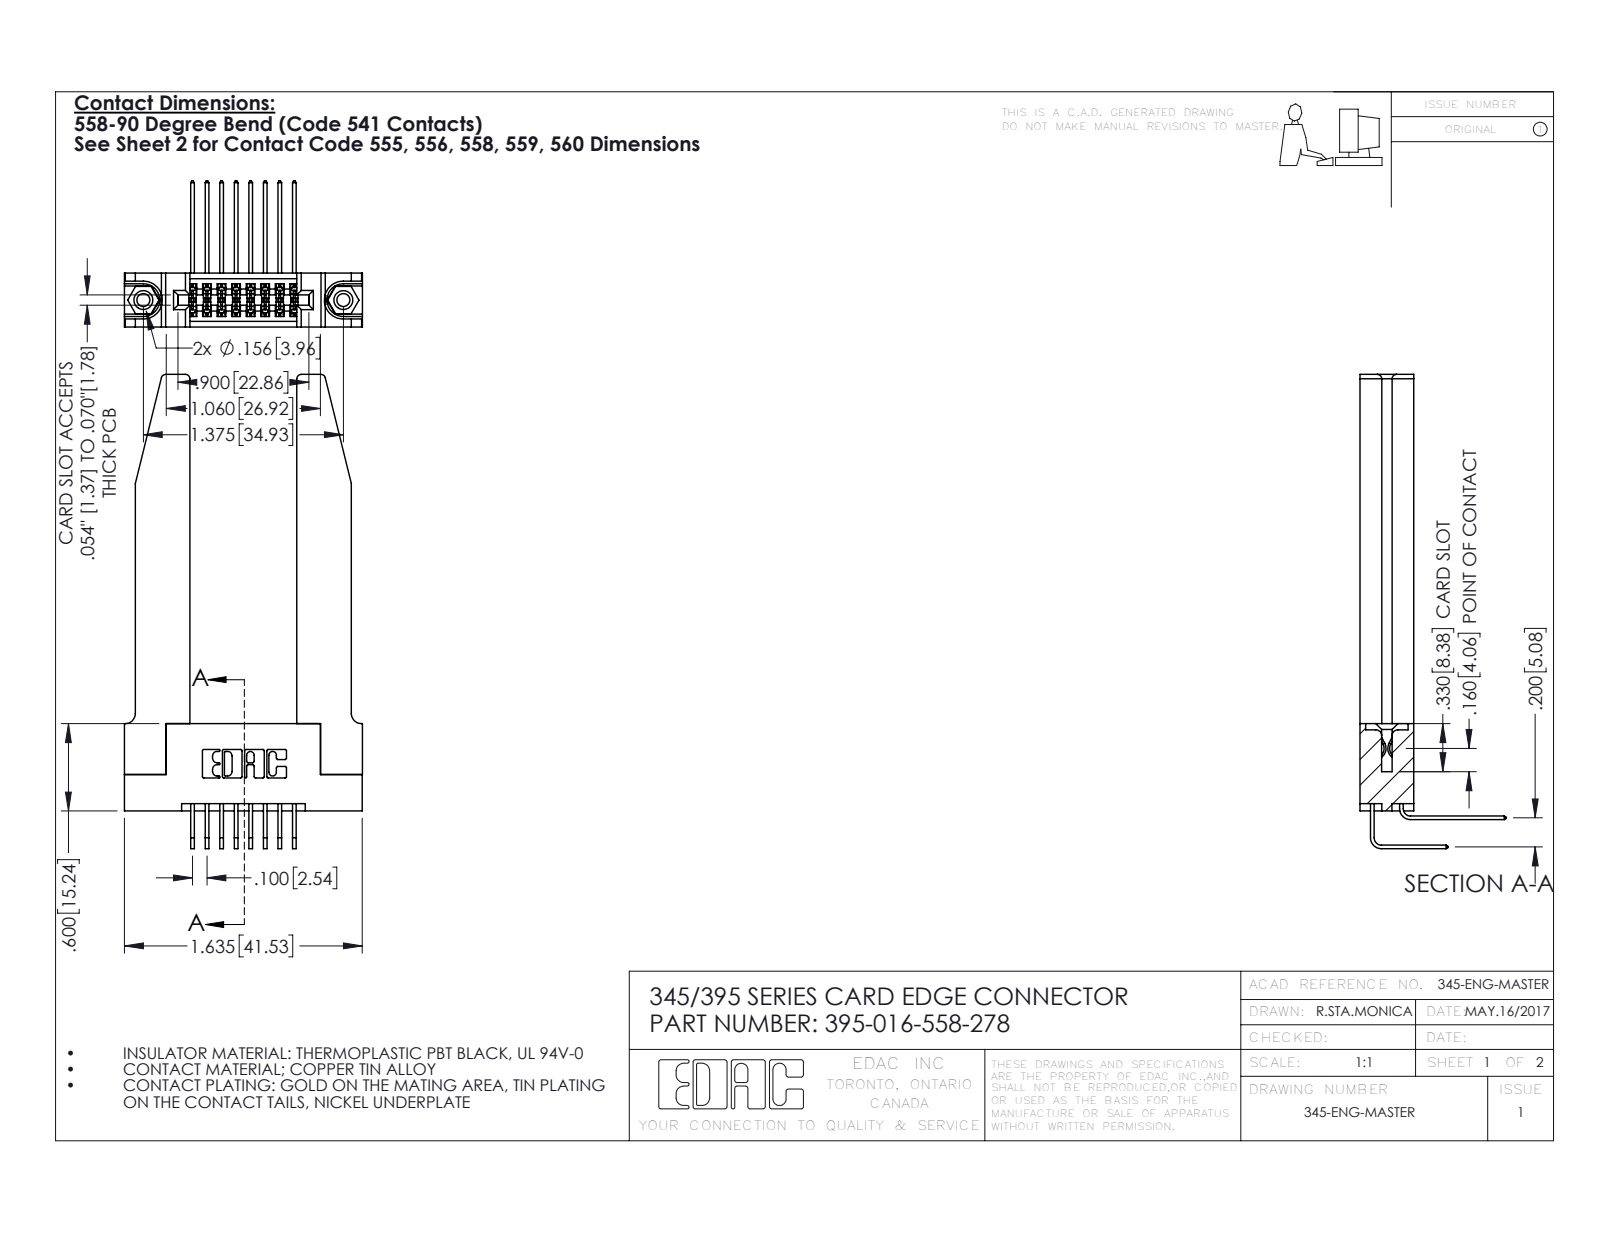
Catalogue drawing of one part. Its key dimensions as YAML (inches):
part_name: "345-292-001_558 Tail - 2; 345 Part_Flush Mounting Lugs - 0.156 Dia-TH; 345-250-001_345-250-001-102; 345-292-001_558 559 Tail - 1 (+2 more)"
step_written_by: "SolidWorks 2016 (CONFIG_CONTROL_DESIGN)"
units: inches
bodies: {solids: 21, faces: 1192, planar: 782, cylindrical: 358, other: 52}
overall_size: [3.259, 1.636, 1.005]
volume: 0.707
surface_area: 18.99
round_holes:
  - {diameter: 0.089, count: 2}
  - {diameter: 0.125, count: 2}
  - {diameter: 0.156, count: 2}
  - {diameter: 0.064, count: 1}
round_bosses_or_shafts:
  - {diameter: 0.155, count: 2}
partial_cylinders:
  - {radius: 0.006, count: 25}
  - {radius: 0.01, count: 22}
  - {radius: 0.03, count: 8}
  - {radius: 0.007, count: 6}
  - {radius: 0.031, count: 6}
  - {radius: 0.026, count: 3}
  - {radius: 0.014, count: 2}
  - {radius: 0.019, count: 2}
face_to_face_distances: [0.37, 0.072, 0.298, 0.2, 0.148, 0.15, 0.077, 0.22, 0.735, 0.098]
hole_center_spacings: [0.27, 1.144, 1.375]
